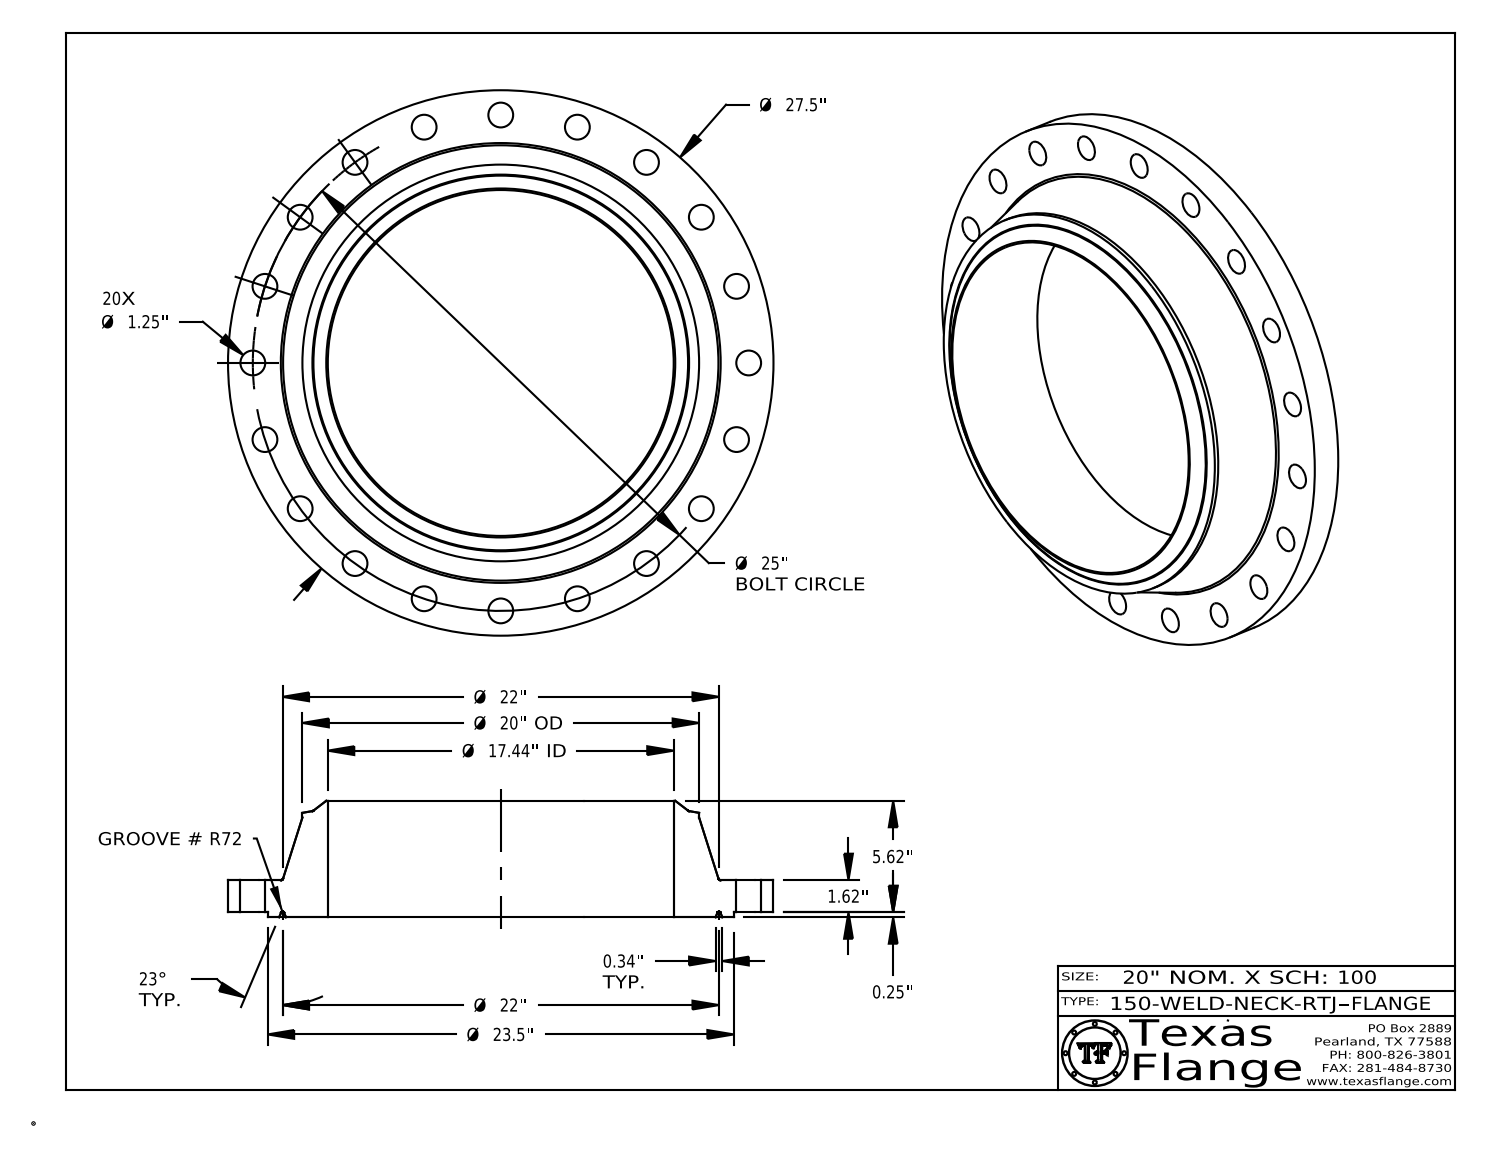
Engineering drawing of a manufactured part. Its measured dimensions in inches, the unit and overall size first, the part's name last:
Units: inches
Overall size (bounding box): 27.5 × 27.5 × 5.87
Round holes (diameter × count): ⌀1.25 ×20, ⌀0.495 ×1, ⌀17.438 ×1
Round bosses / shafts (diameter × count): ⌀0.03 ×8, ⌀27.5 ×1, ⌀23.5 ×1, ⌀20 ×1, ⌀0.39 ×1
Main face-to-face distances: 1.87, 0.25, 1.62, 5.87, 5.62, 4, 1.865, 1.615, 4.005, 0.148
Hole centre spacings: 12.5, 14.694, 17.678, 20.225, 23.776, 24.692, 11.35, 22.275
Volume: 955.8 in³ · Surface area: 1 467 in²
Bodies: 1 solid, 457 faces (371 planar, 68 cylindrical, 18 other)
Part name (STEP PRODUCT): 150-WELD-NECK-RTJ
STEP written by: CATIA V5 STEP AP214 (AUTOMOTIVE_DESIGN)
